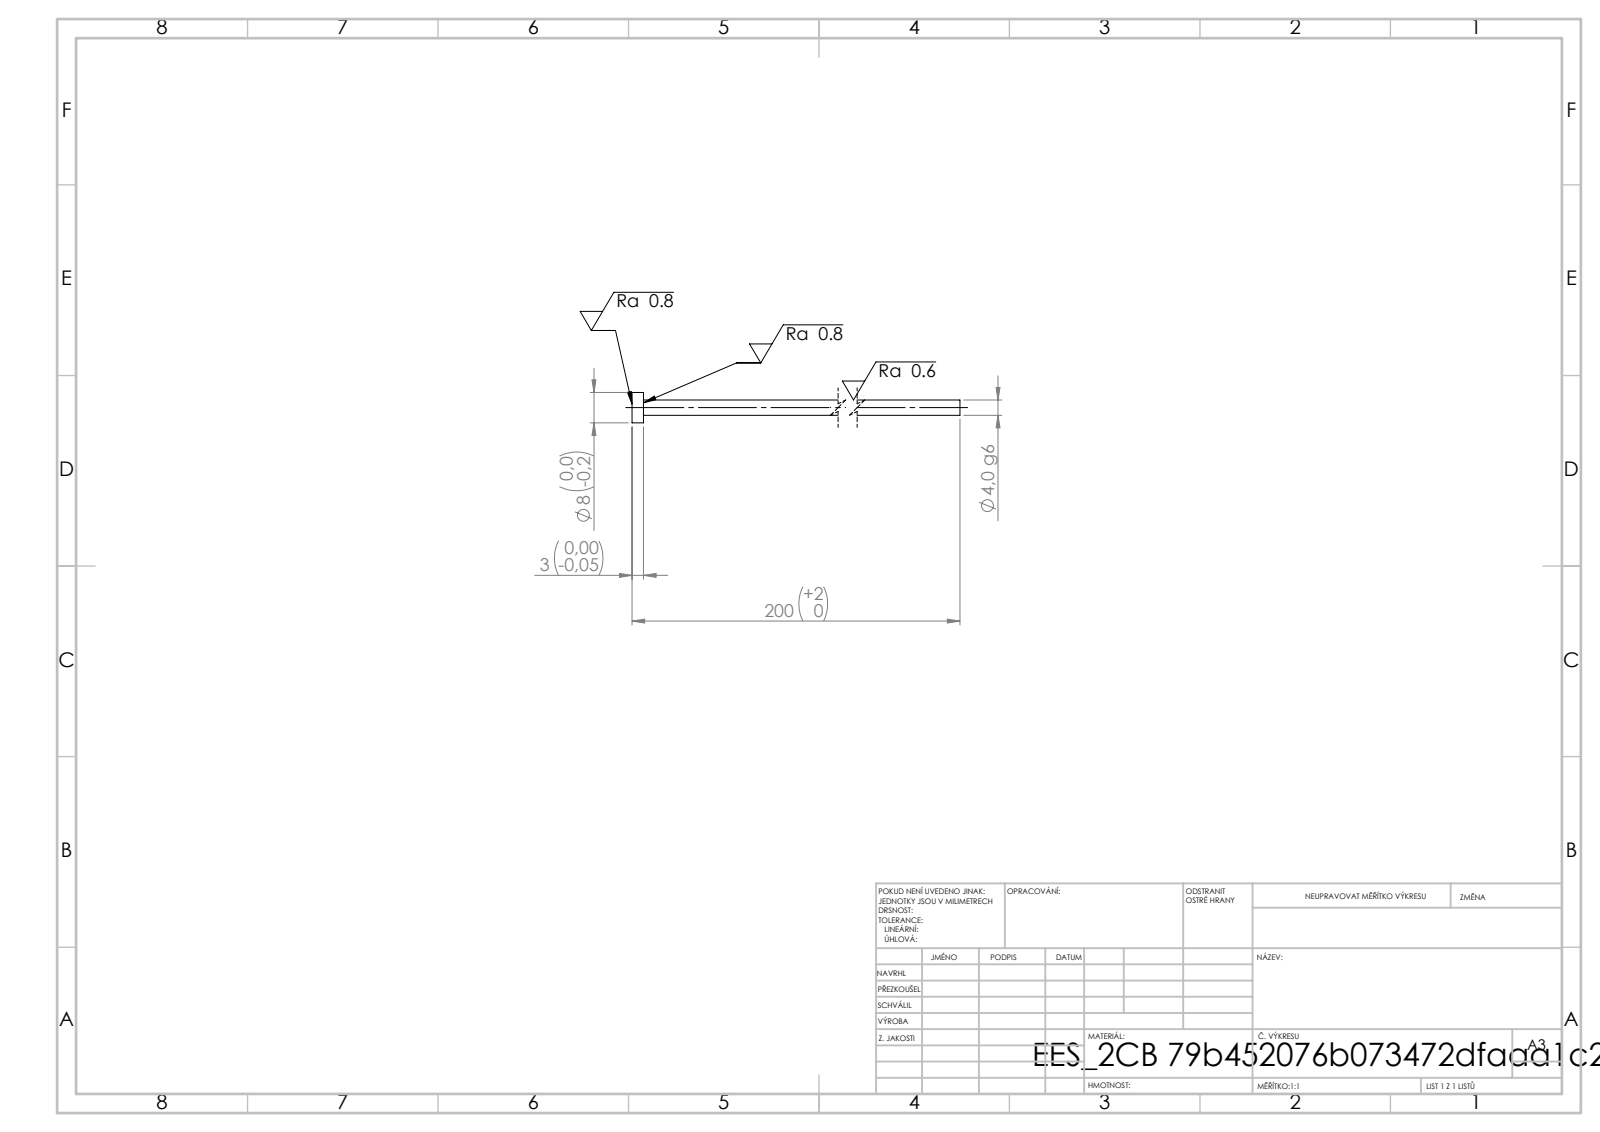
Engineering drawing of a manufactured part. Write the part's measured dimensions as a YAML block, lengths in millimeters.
step_written_by: "SolidWorks 2019 (CONFIG_CONTROL_DESIGN)"
units: millimeters
bodies: {solids: 1, faces: 7, planar: 3, cylindrical: 4, other: 0}
overall_size: [200, 8, 8]
volume: 2626
surface_area: 2652
round_bosses_or_shafts:
  - {diameter: 8, count: 1}
  - {diameter: 4, count: 1}
face_to_face_distances: [3, 200, 197]
